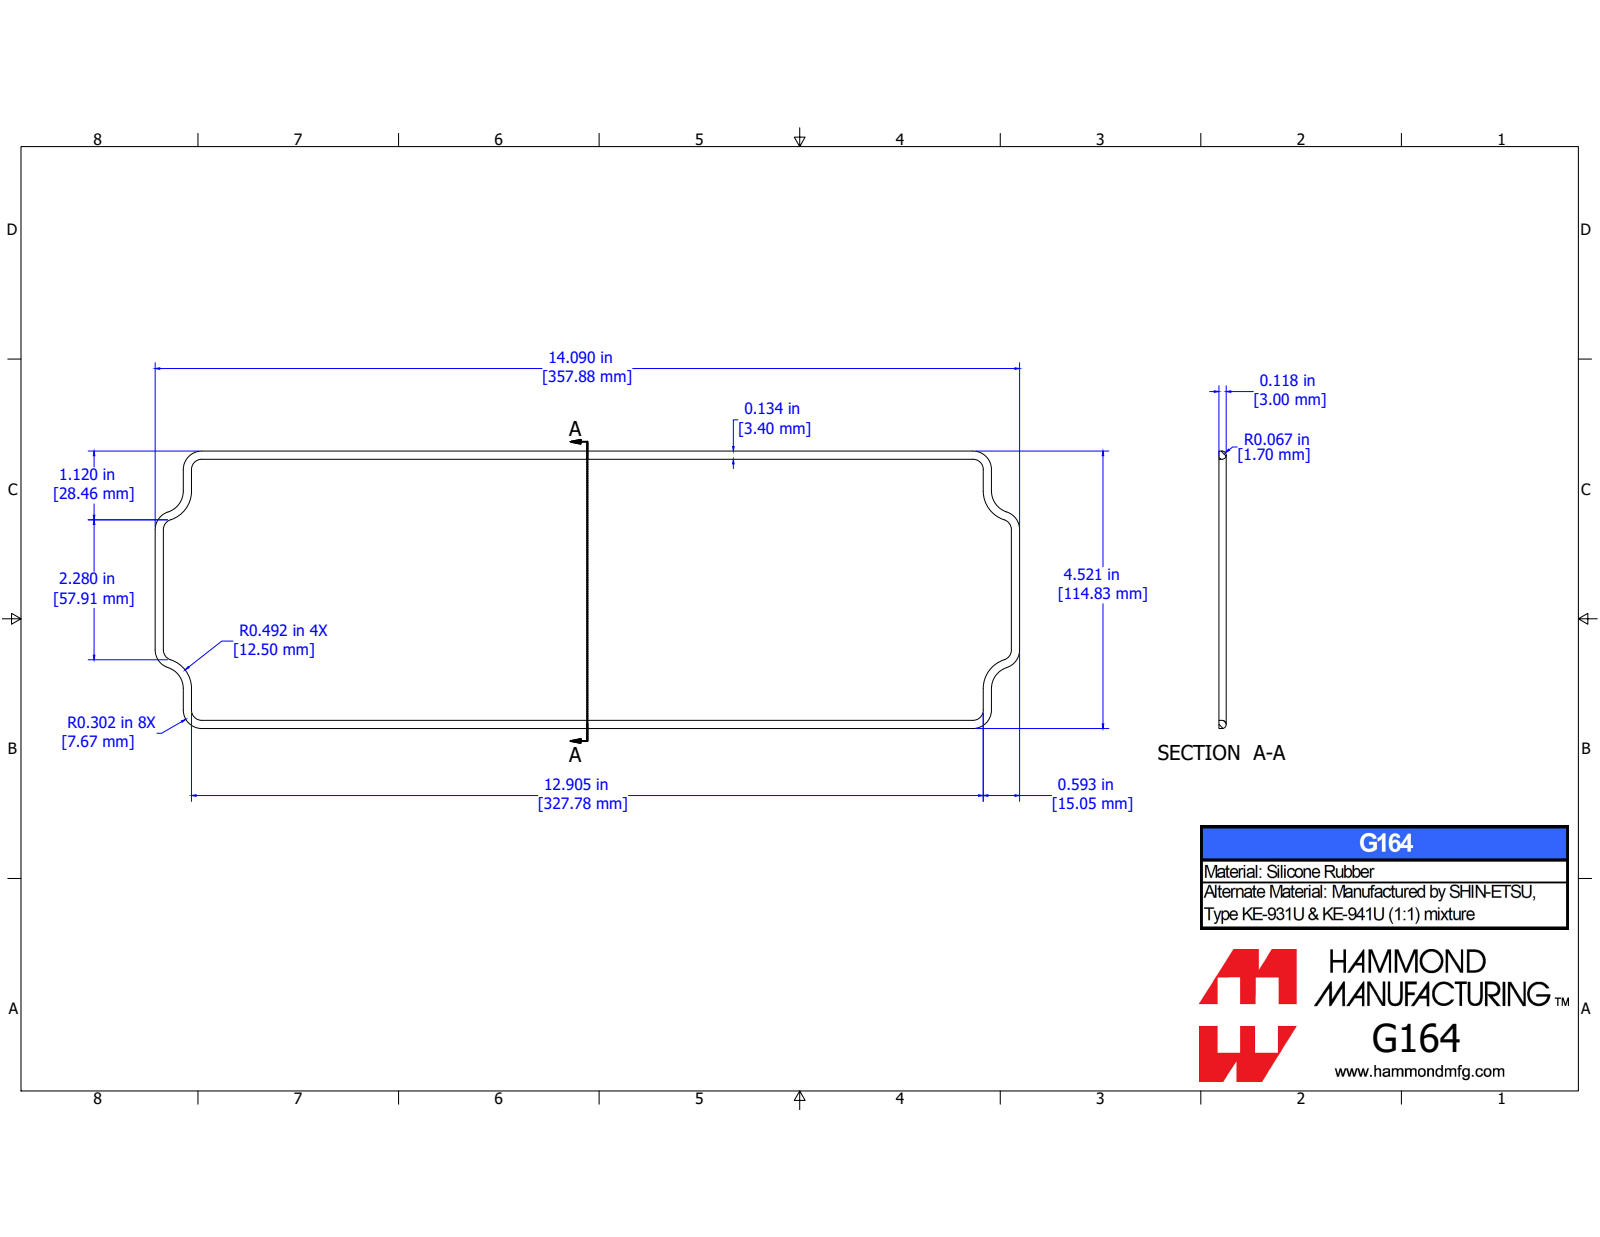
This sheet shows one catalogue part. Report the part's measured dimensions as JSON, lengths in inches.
{"part_name": "1590Z164G", "step_written_by": "SolidWorks 2019 (CONFIG_CONTROL_DESIGN)", "units": "inches", "bodies": {"solids": 1, "faces": 82, "planar": 18, "cylindrical": 16, "other": 48}, "overall_size": [14.039, 4.681, 0.138], "volume_in3": 0.673, "surface_area_in2": 18.61, "partial_cylinders_radius": [[0.059, 12]], "face_to_face_distances": [4.531, 0.138, 13.89, 0.457, 13.433, 12.976]}
